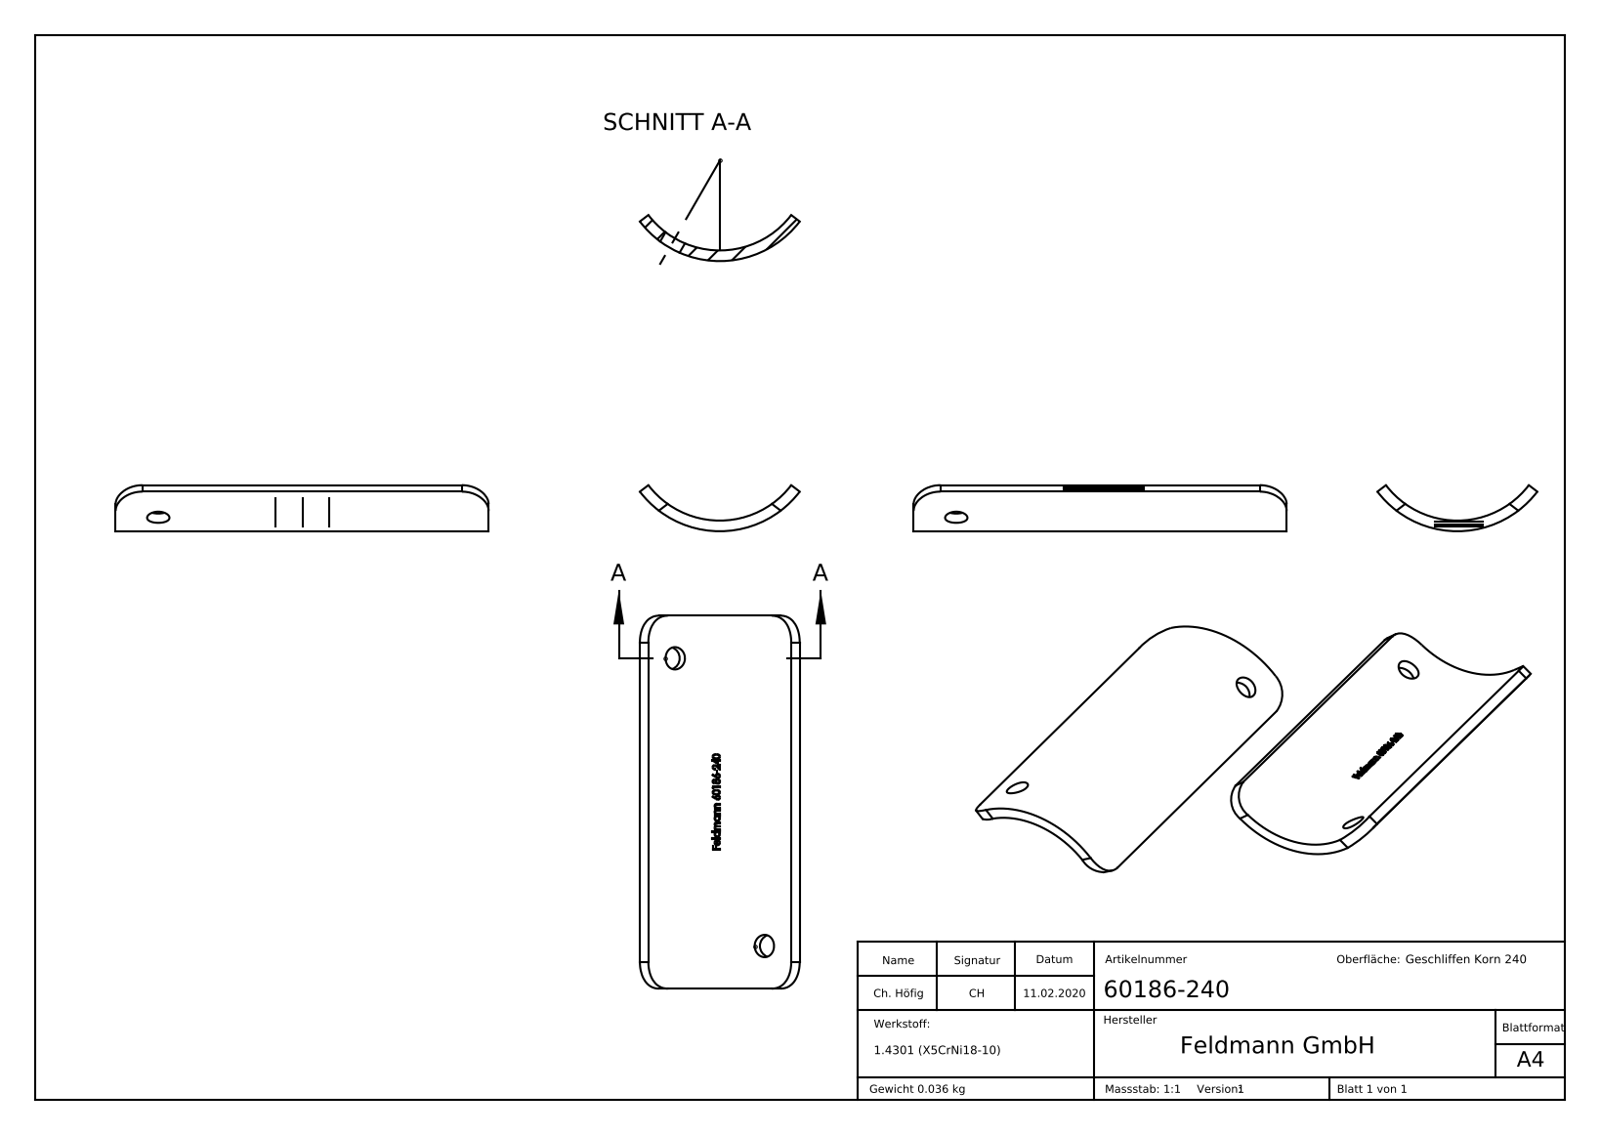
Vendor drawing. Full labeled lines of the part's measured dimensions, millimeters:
Part name (STEP PRODUCT): 60186-240
STEP written by: SolidWorks 2015 (CONFIG_CONTROL_DESIGN)
Units: millimetres
Bodies: 1 solid, 235 faces (93 planar, 35 cylindrical, 107 other)
Overall size (bounding box): 70 × 30 × 8.64
Volume: 4 500 mm³ · Surface area: 4 958 mm²
Round holes (diameter × count): ⌀4.2 ×2
Partial cylindrical surfaces — rounded edges, fillets, slot ends (radius × count): R5 ×4, R16.85 ×1, R16.95 ×1, R18.85 ×1
Main face-to-face distances: 70, 0.39, 2.97, 11.73, 14.62, 8.46, 3.27, 0.44, 0.88, 8.07
